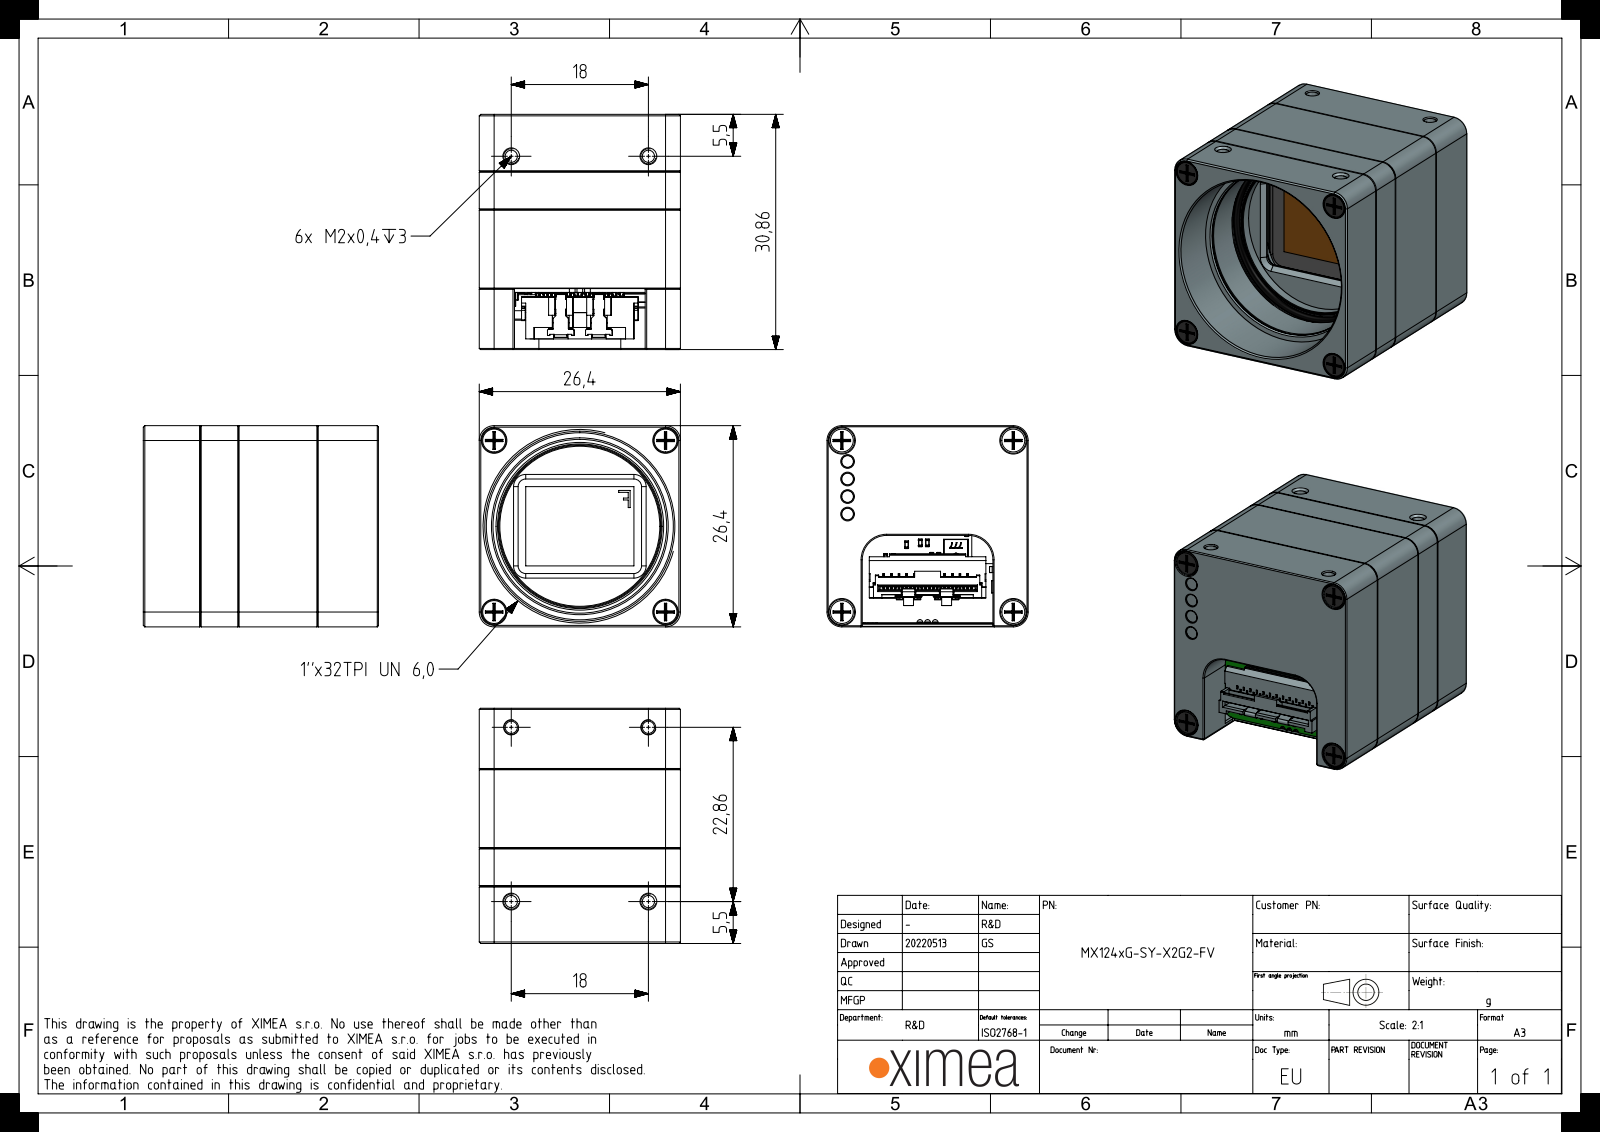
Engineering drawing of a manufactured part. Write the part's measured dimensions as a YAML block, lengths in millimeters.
part_name: "MT124xG-PR-SENSOR-PCA; MECH-O-RING-22X1-VI370; FLT-BK7-AR2X-D25; SROB-M1.6x3-SLOT-STNLS (+8 more)"
step_written_by: "SIEMENS PLM Software NX 1907 (AUTOMOTIVE_DESIGN)"
units: millimeters
bodies: {solids: 31, faces: 7537, planar: 5246, cylindrical: 2016, other: 275}
overall_size: [30.9, 26.4, 26.4]
volume: 10400
surface_area: 17910
round_holes:
  - {diameter: 1.6, count: 12}
  - {diameter: 0.9, count: 4}
  - {diameter: 2, count: 4}
  - {diameter: 2.1, count: 4}
  - {diameter: 3, count: 4}
  - {diameter: 3.2, count: 4}
  - {diameter: 3.4, count: 4}
  - {diameter: 1.3, count: 2}
  - {diameter: 1.7, count: 2}
  - {diameter: 21, count: 1}
  - {diameter: 22.8, count: 1}
  - {diameter: 24.4, count: 1}
round_bosses_or_shafts:
  - {diameter: 1.9, count: 4}
  - {diameter: 1.6, count: 4}
  - {diameter: 0.8, count: 4}
  - {diameter: 3, count: 2}
  - {diameter: 1.6, count: 2}
  - {diameter: 25, count: 1}
  - {diameter: 21.6, count: 1}
partial_cylinders:
  - {radius: 0.3, count: 16}
  - {radius: 1.5, count: 15}
  - {radius: 0.2, count: 14}
  - {radius: 1, count: 14}
  - {radius: 0.1, count: 12}
  - {radius: 0.4, count: 12}
  - {radius: 0.3, count: 8}
  - {radius: 0.5, count: 8}
face_to_face_distances: [1, 26.4, 3.6, 11.5, 6.9, 2.5, 4.6, 10.5, 10.4, 6.8]
hole_center_spacings: [15.9, 22.5, 2.3, 3.8, 4.6, 13.5, 18, 18.7]
